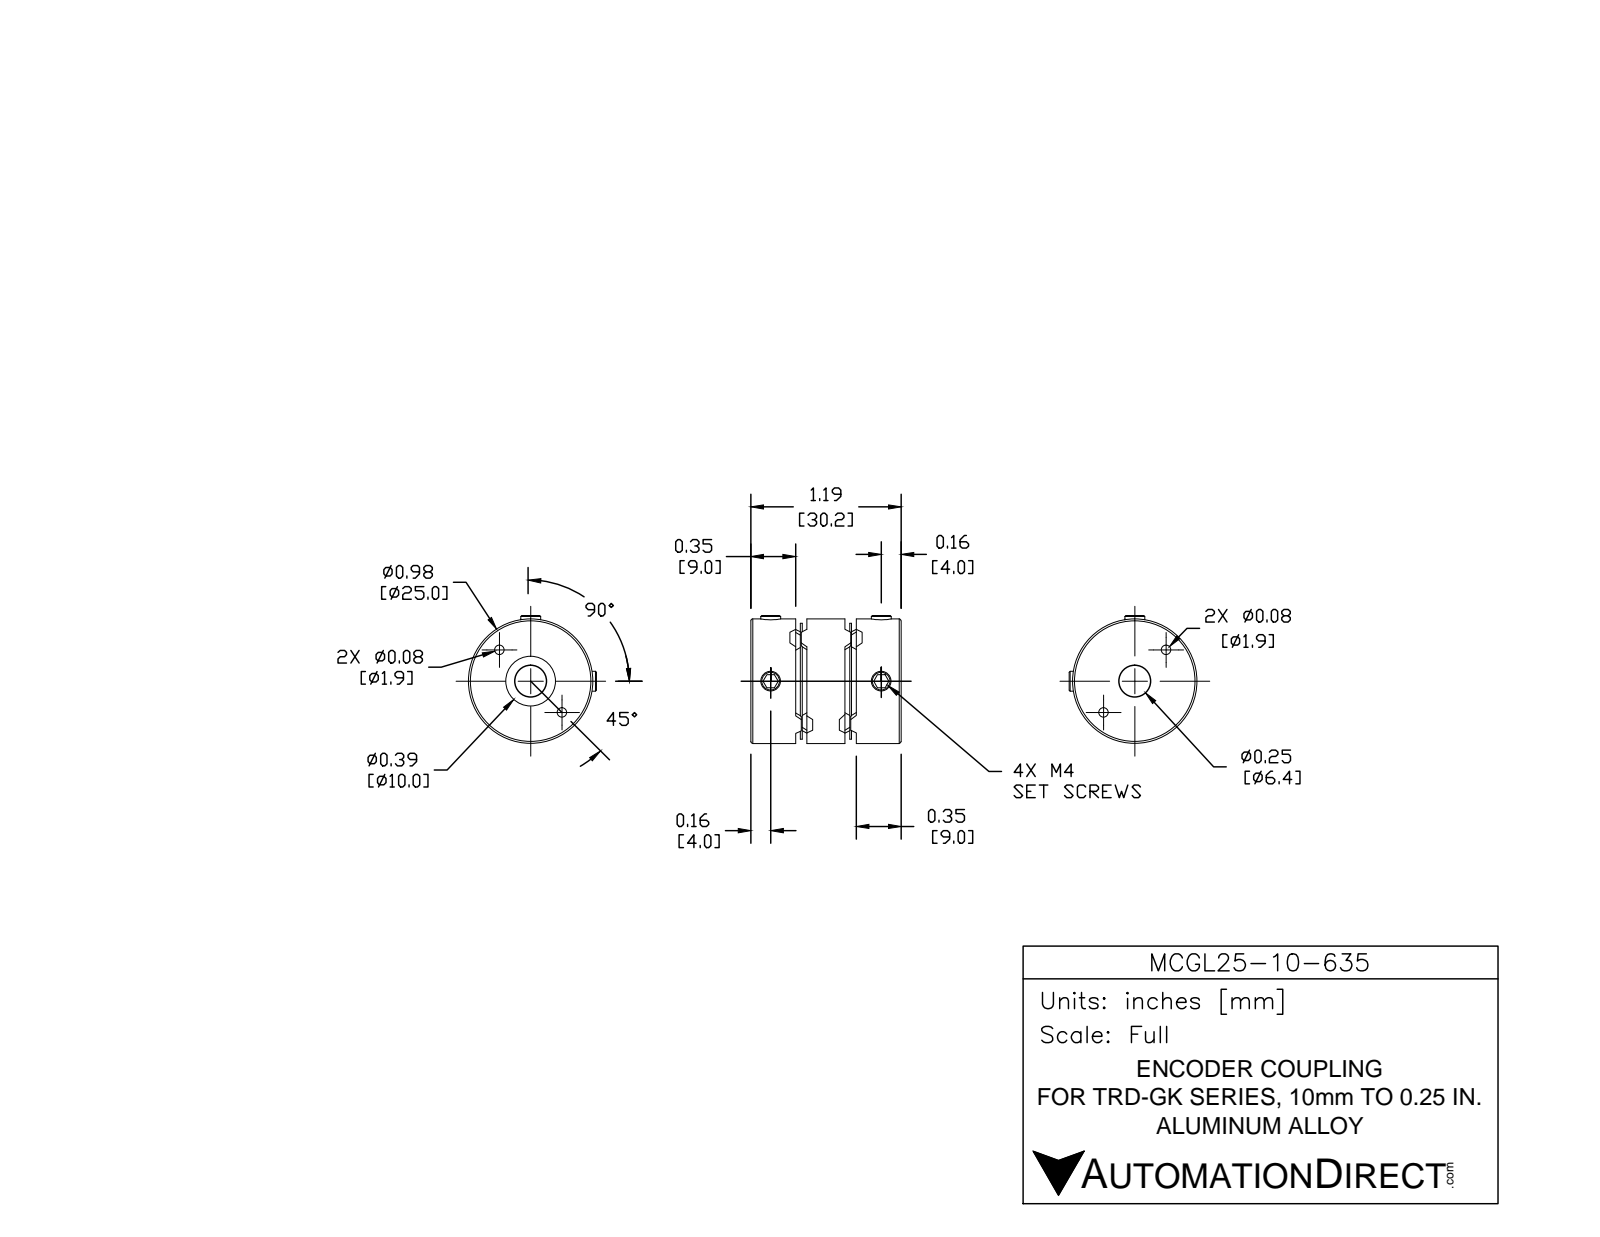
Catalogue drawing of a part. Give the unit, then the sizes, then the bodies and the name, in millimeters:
Units: millimetres
Overall size (bounding box): 30 × 25 × 25
Round holes (diameter × count): ⌀4 ×4, ⌀3.6 ×2, ⌀6.35 ×1, ⌀10 ×1, ⌀12 ×1
Round bosses / shafts (diameter × count): ⌀25 ×1
Main face-to-face distances: 1.5, 8.4, 2.1, 10.5, 9, 12.6, 17.4, 11.1, 18.9, 6.3
Hole centre spacings: 9.4, 22, 18.8
Volume: 9 991 mm³ · Surface area: 7 081 mm²
Bodies: 1 solid, 142 faces (70 planar, 36 cylindrical, 36 other)
Part name (STEP PRODUCT): MCGL25-10-635
STEP written by: SolidWorks 2016 (AUTOMOTIVE_DESIGN)
